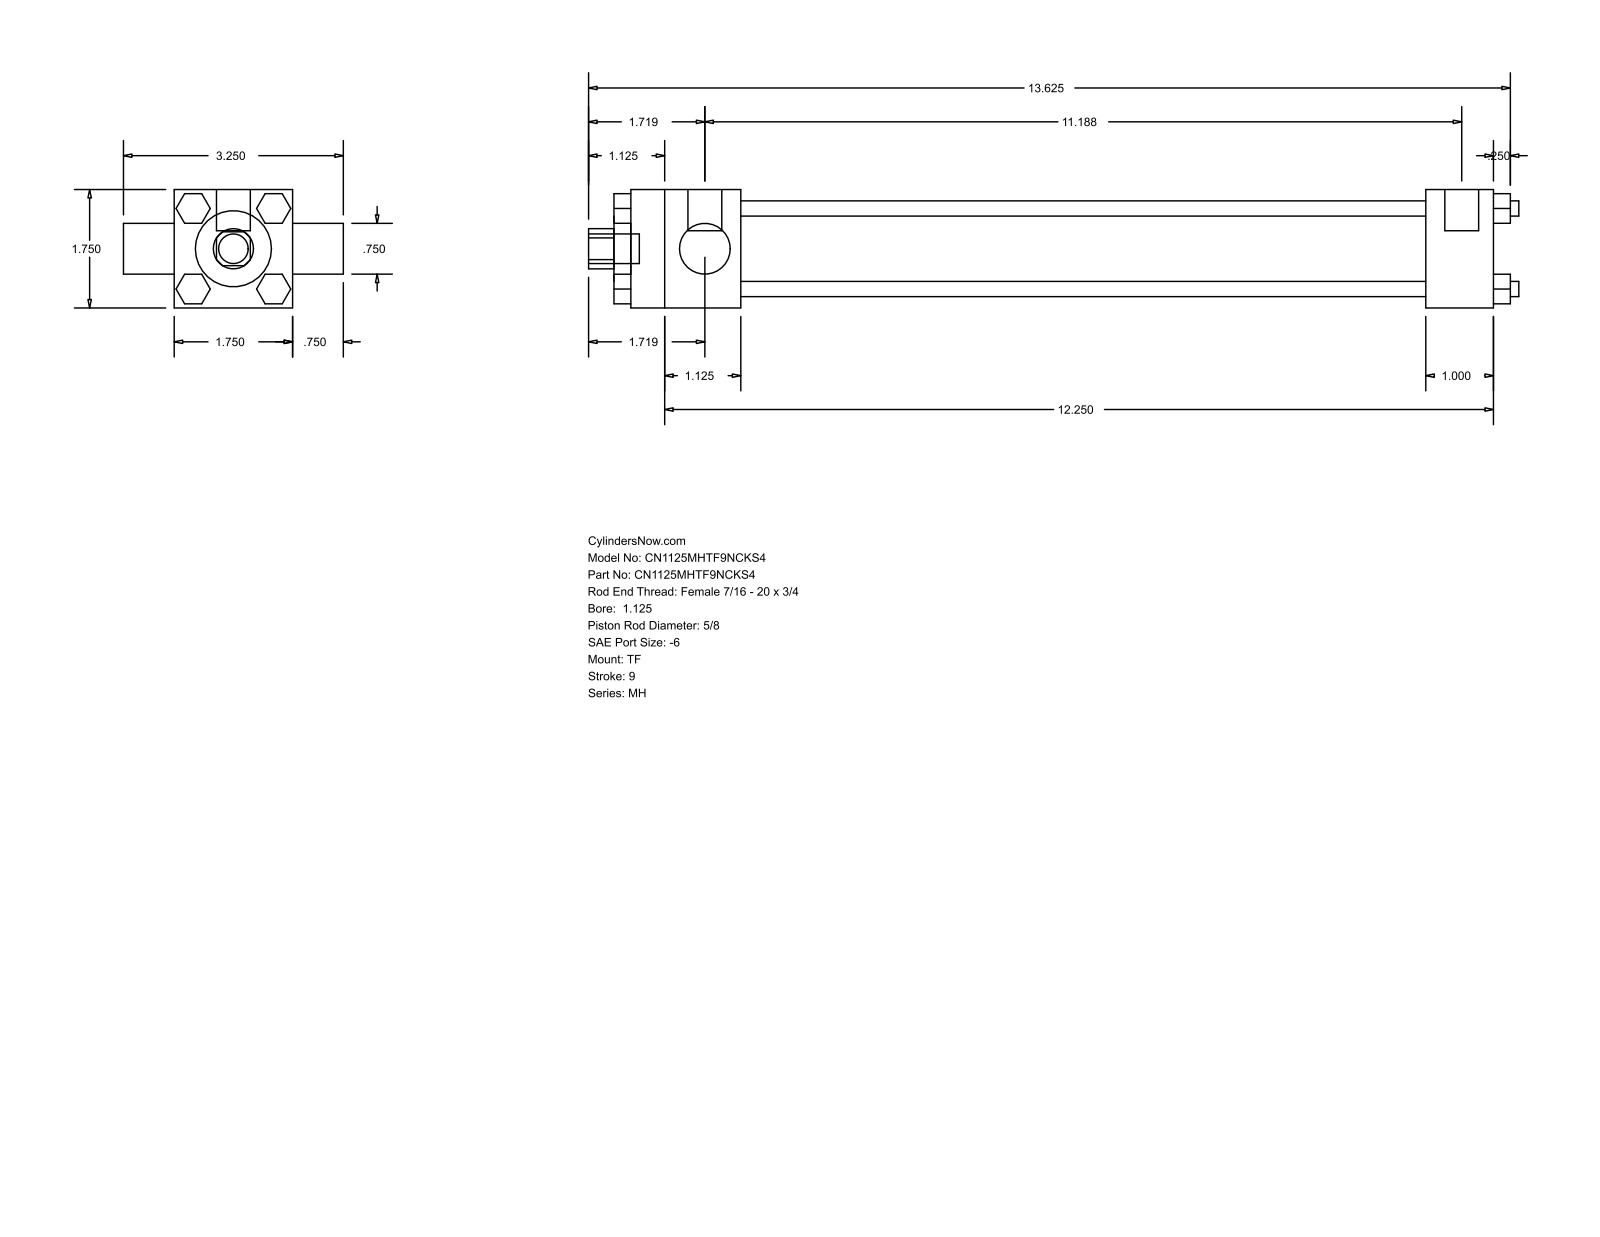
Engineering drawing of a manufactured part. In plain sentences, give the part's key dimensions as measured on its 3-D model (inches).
The part is named "MH_TF__0112_0.625". Its 3-D file was written by "GSSL Pune (CONFIG_CONTROL_DESIGN)". It is 0 solids with 120 faces: 92 planar, 28 cylindrical and 0 other. Overall it measures 13.75 by 3.25 by 1.75 inches. Round holes: 1 of diameter 0.625, 1 of diameter 0.75, 1 of diameter 1.125, 1 of diameter 1.375. Round bosses or shafts: 4 of diameter 0.225, 3 of diameter 0.219, 2 of diameter 0.5, 1 of diameter 0.437. Partial cylindrical surfaces (rounded edges, fillets, slot ends): 1 of radius 0.297. The main face-to-face distances are 1.75, 0.437, 10.125, 11.125, 1, 1.625, 11.75, 12.75, 1.875, 13.
